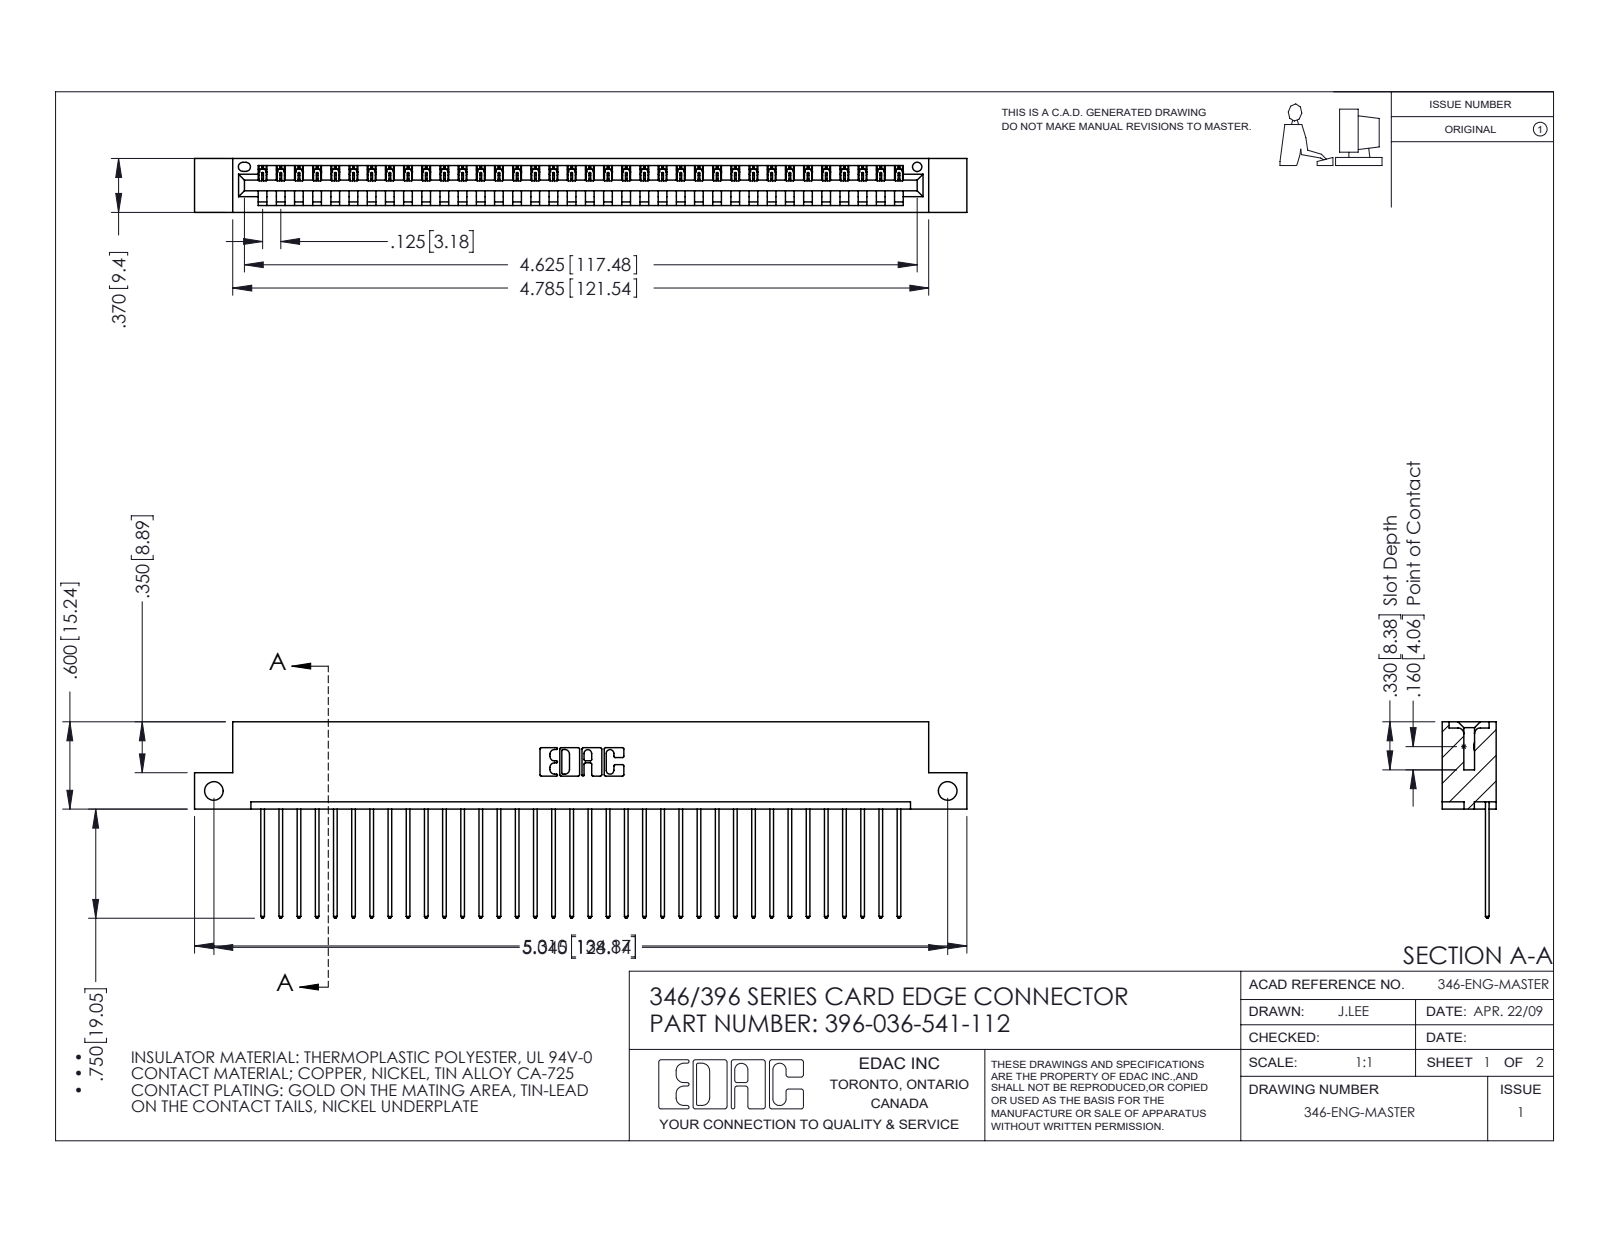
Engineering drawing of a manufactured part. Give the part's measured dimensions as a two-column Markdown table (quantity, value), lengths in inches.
| quantity | value |
| --- | --- |
| part name | 396-036-541-112; 346 Part_Flush Mounting Lugs - Side Mount; 345-292-001_345-293-141 |
| STEP written by | SolidWorks 2016 (CONFIG_CONTROL_DESIGN) |
| units | inches |
| bodies | 37 solids, 2210 faces (1516 planar, 694 cylindrical, 0 other) |
| overall size | 5.31 × 1.35 × 0.37 |
| volume | 0.787 in³ |
| surface area | 25.77 in² |
| round holes (diameter × count) | 0.128 × 2, 0.064 × 1 |
| partial cylindrical surfaces (radius × count) | 0.006 × 72, 0.01 × 72, 0.01 × 22, 0.007 × 6, 0.031 × 6, 0.026 × 3, 0.031 × 2, 0.04 × 2 |
| main face-to-face distances | 0.048, 0.322, 0.37, 0.25, 0.072, 0.298, 0.025, 0.148, 0.222, 0.1 |
| hole center spacings | 5.045 |
